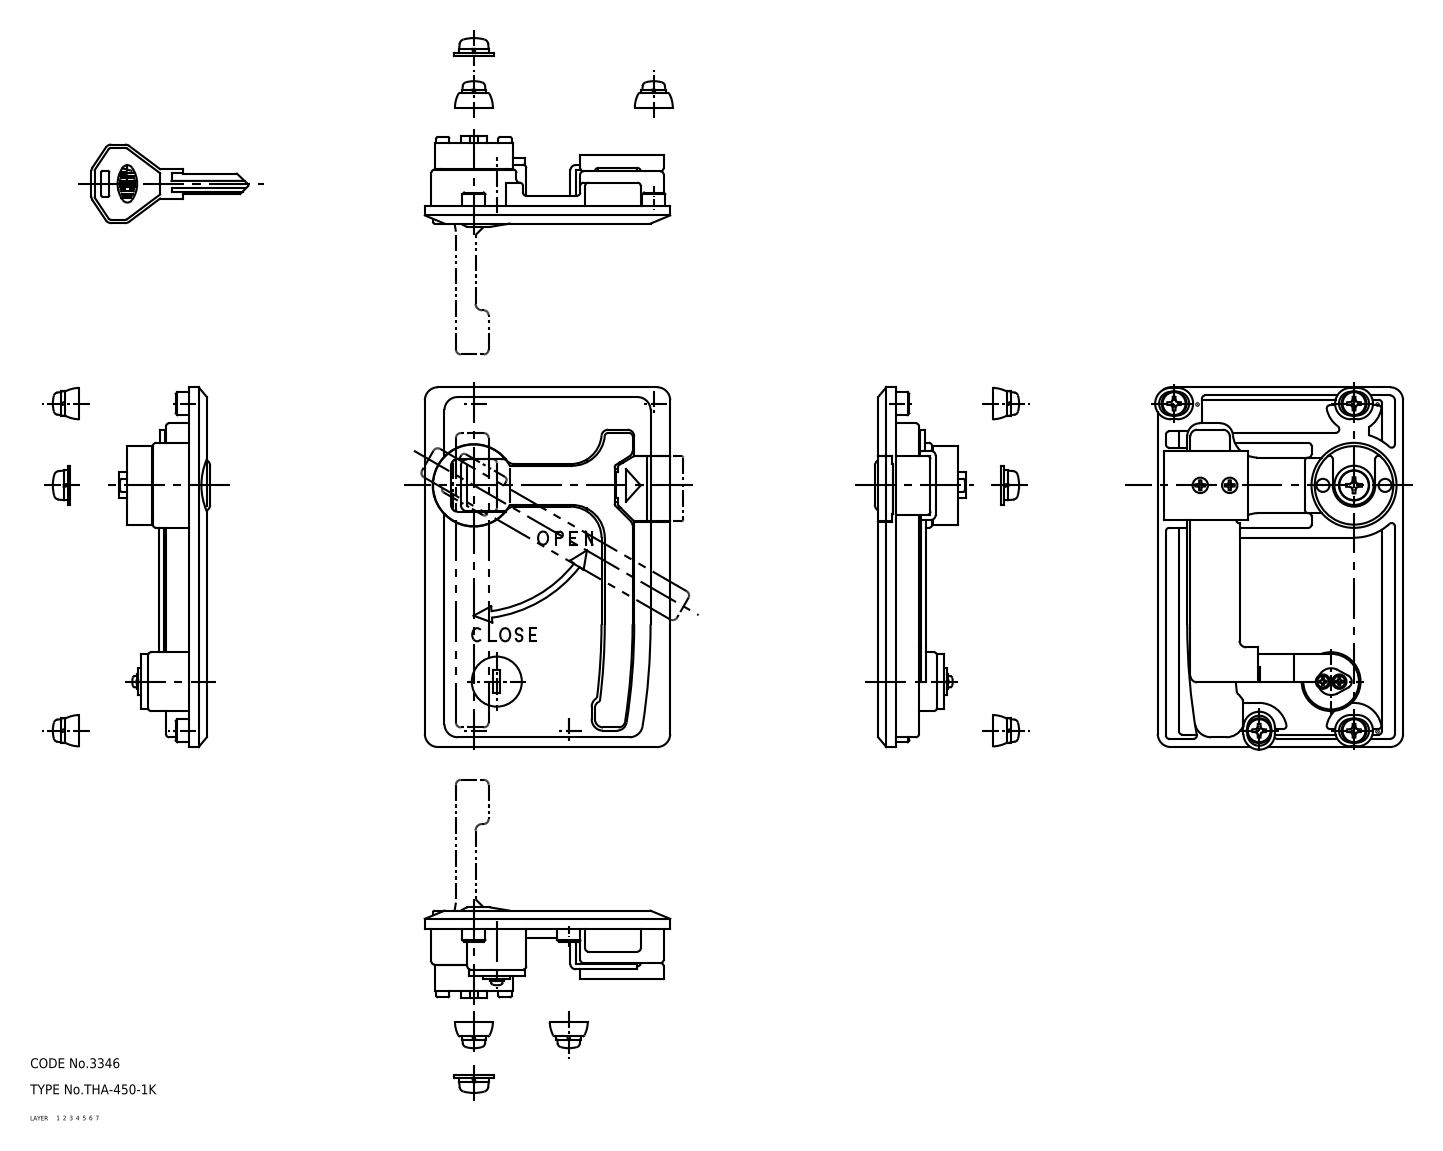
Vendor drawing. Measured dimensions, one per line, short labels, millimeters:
name: screw_C; screw_A; bracket; shaft_2 (+8 more)
written by: CADfix (AUTOMOTIVE_DESIGN)
unit: mm
bodies: 21 solids, 851 faces (0 planar, 0 cylindrical, 851 other)
size: 110.8 × 110.42 × 108.8
volume: 63 972 mm³; area: 56 665 mm²
